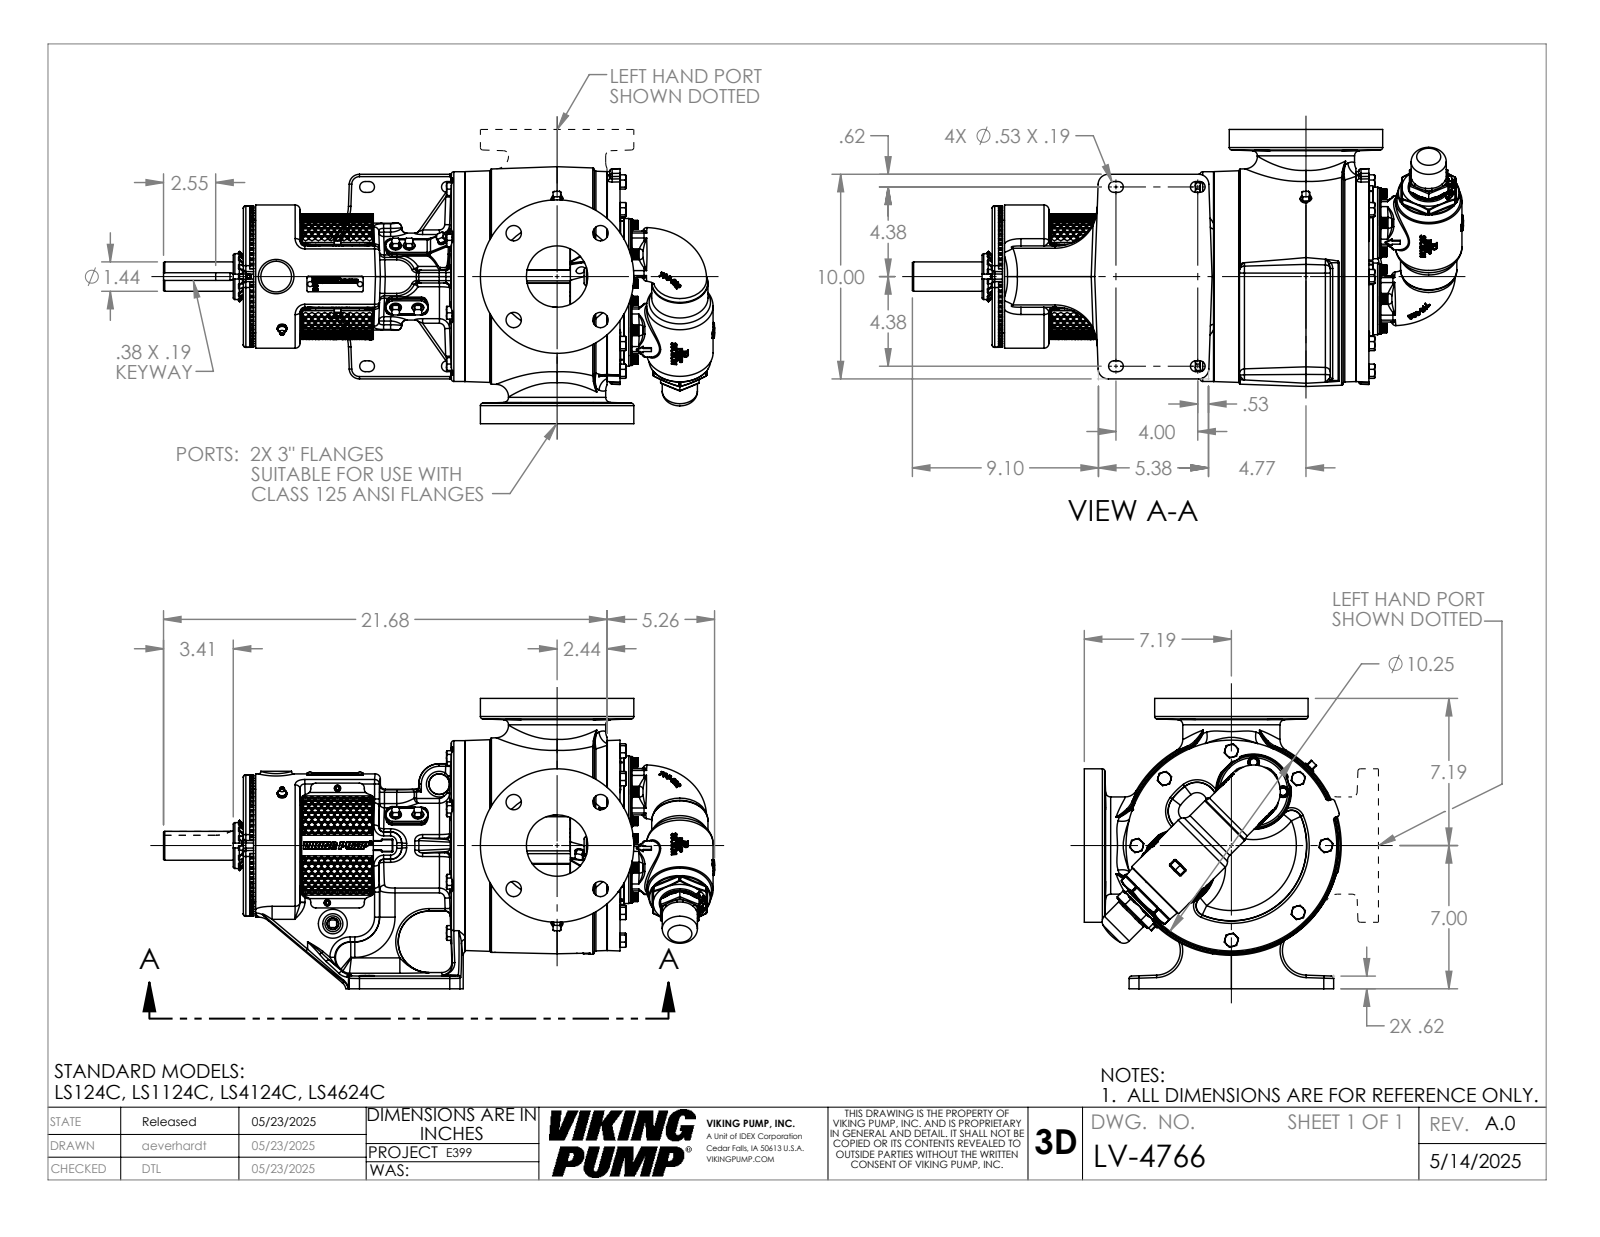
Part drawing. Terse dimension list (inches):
name: LV-4766
written by: SolidWorks 2024 (AUTOMOTIVE_DESIGN)
unit: in
bodies: 1 solid, 5226 faces (1738 planar, 1048 cylindrical, 2440 other)
size: 26.939 × 14.19 × 12.56
volume: 1 125 in³; area: 1 504 in²
holes: 8× ⌀0.75, 8× ⌀1.094, 6× ⌀0.199, 6× ⌀0.25, 3× ⌀0.159, 2× ⌀0.266, 2× ⌀0.313, 1× ⌀1.506, 1× ⌀1.552, 1× ⌀1.577, 1× ⌀1.593, 1× ⌀1.83
bosses: 13× ⌀0.625, 8× ⌀0.563, 3× ⌀0.625, 3× ⌀0.437, 3× ⌀0.312, 2× ⌀7.5, 2× ⌀4.75, 2× ⌀3.5
rounds: 109× R0.063, 74× R0.069, 74× R0.12, 48× R0.24, 38× R0.03, 16× R0.45, 14× R0.5, 12× R0.25
face distances: 14.19, 1.5, 15.664, 3.534, 12.13, 0.5, 2.25, 2.146, 5.68, 17.81
hole spacings: 3, 4.243, 1.375, 2.18, 3.609, 4.446, 4.625, 6.404
